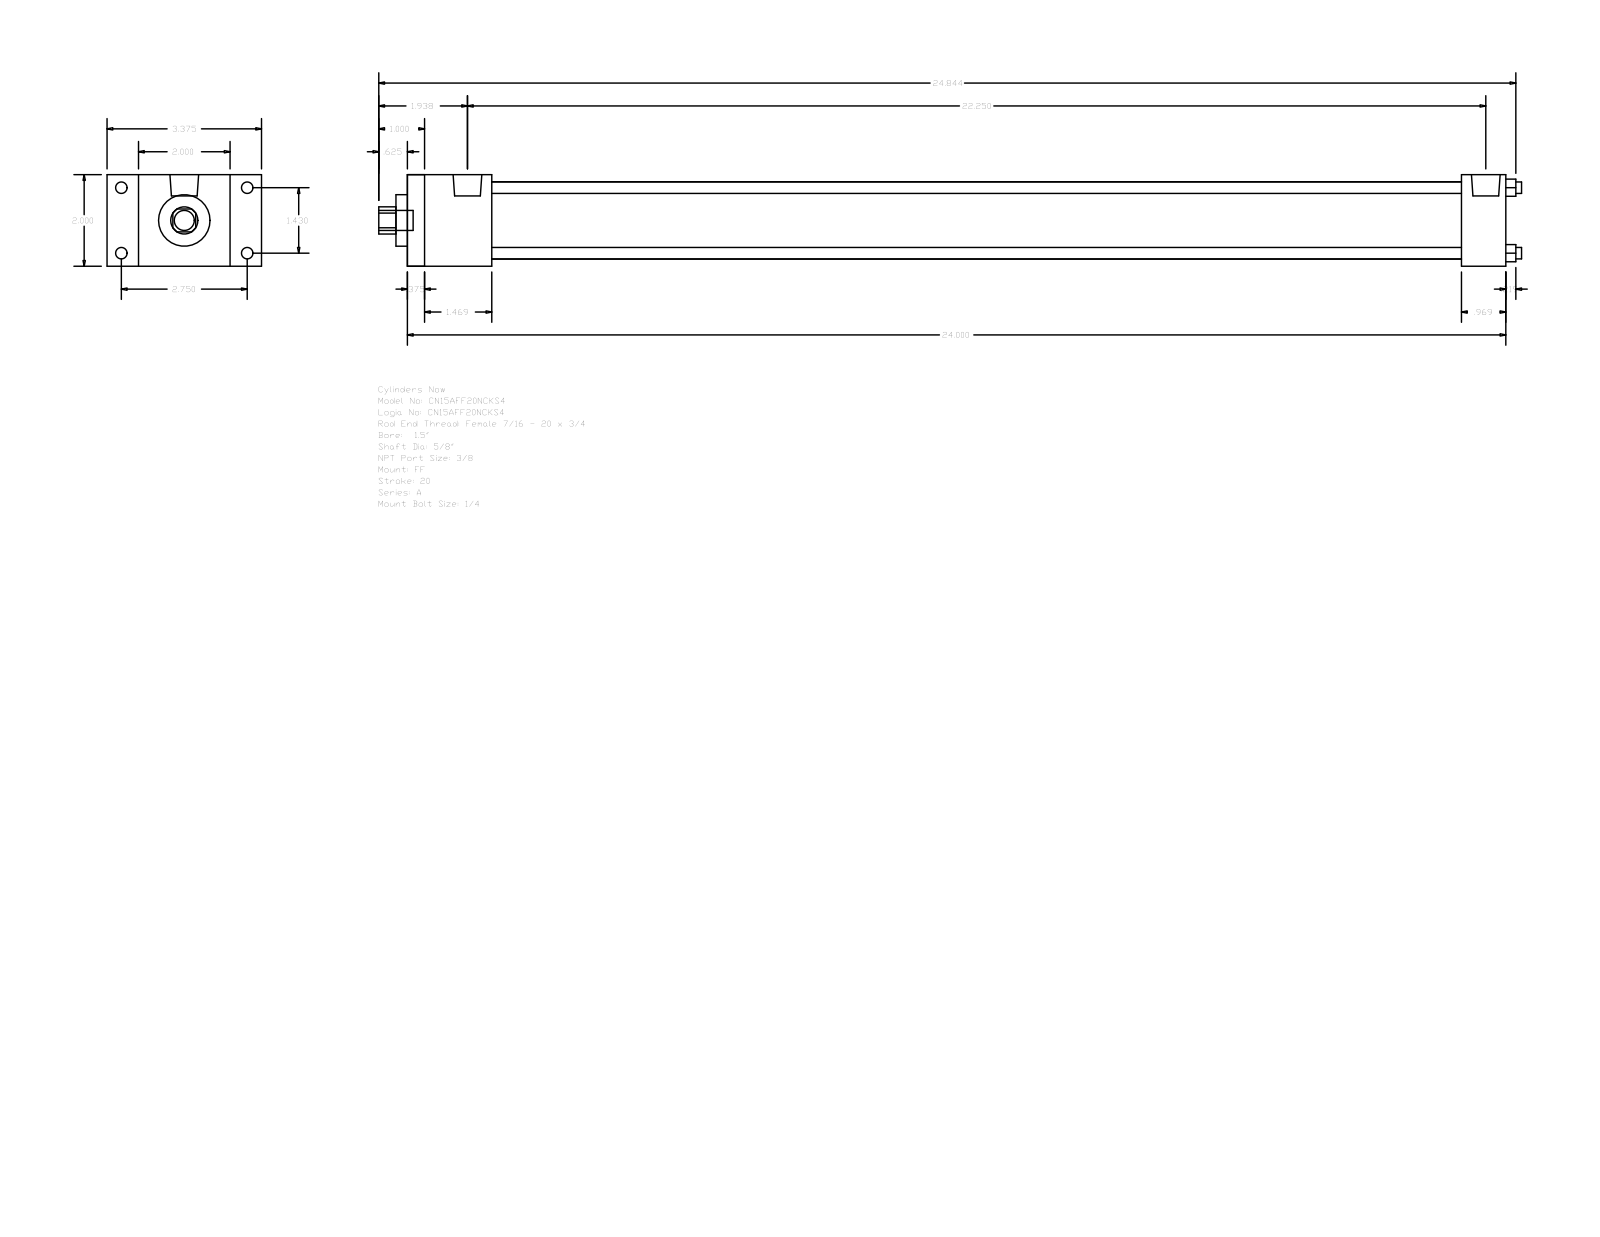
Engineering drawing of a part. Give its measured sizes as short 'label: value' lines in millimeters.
name: A_FF__0150_0.625
written by: GSSL Pune (CONFIG_CONTROL_DESIGN)
unit: mm
bodies: 0 solids, 92 faces (64 planar, 28 cylindrical, 0 other)
size: 634.21 × 85.72 × 50.8
holes: 4× ⌀6.35, 1× ⌀15.88, 1× ⌀28.57, 1× ⌀42.93
bosses: 4× ⌀6.35, 4× ⌀5.56, 2× ⌀15.93, 1× ⌀11.11
rounds: 1× R7.54
face distances: 50.8, 609.6, 9.52, 600.08, 46.83, 584.99, 37.31, 575.47, 538.16, 562.77
hole spacings: 25.68, 36.32, 51.36
